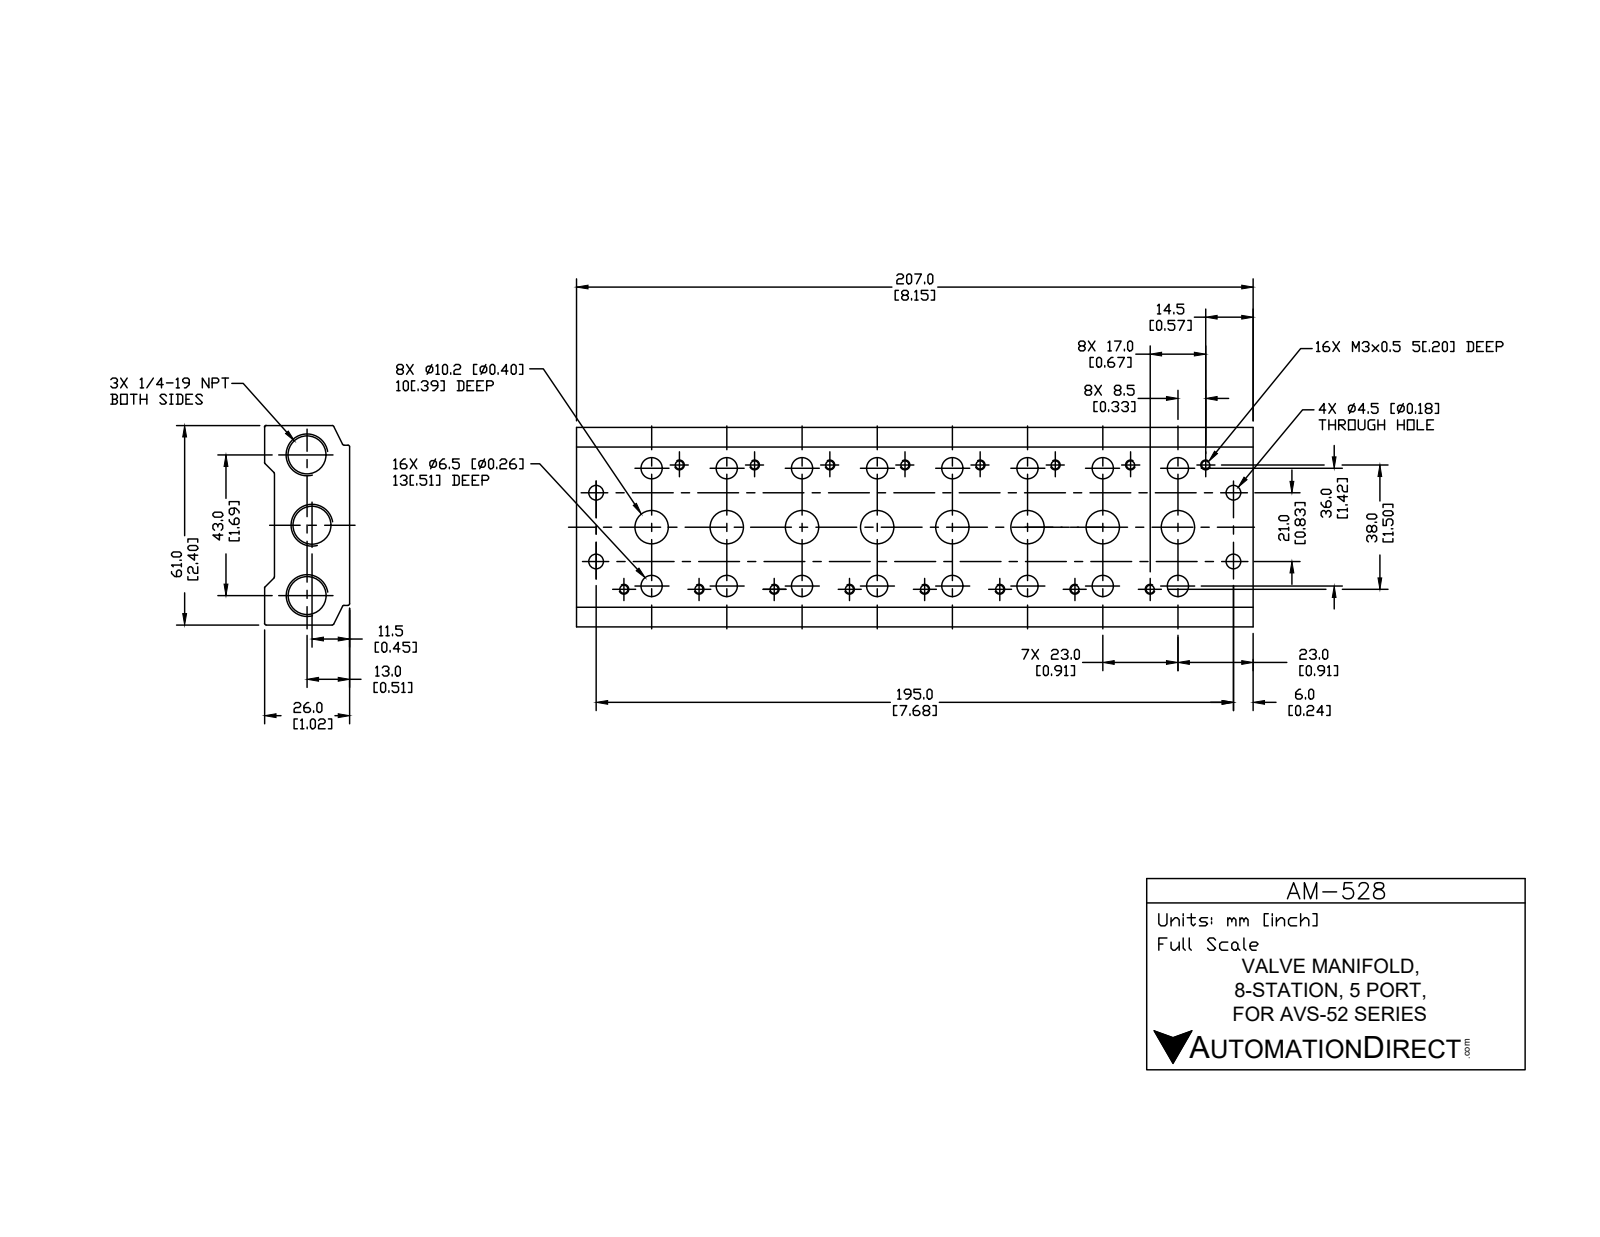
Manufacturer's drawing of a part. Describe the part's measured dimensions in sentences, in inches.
The part is named "AM-528". Its 3-D file was written by "SolidWorks 2015 (CONFIG_CONTROL_DESIGN)". It is 1 solid with 185 faces: 36 planar, 105 cylindrical and 44 other. Overall it measures 8.15 by 2.402 by 1.024 inches. Its volume is 13.81 cubic inches and its surface area 100.1 square inches. Round holes: 16 of diameter 0.098, 16 of diameter 0.256, 8 of diameter 0.402, 4 of diameter 0.177, 3 of diameter 0.438. Partial cylindrical surfaces (rounded edges, fillets, slot ends): 11 of radius 0.02. The main face-to-face distances are 0.906, 2.402, 0.118, 1.024, 8.15, 0.236, 2.165, 0.394, 7.755, 1.929. The hole center spacings are 0.906, 1.811, 0.337, 1.494, 2.717, 3.622, 4.528, 0.572.
